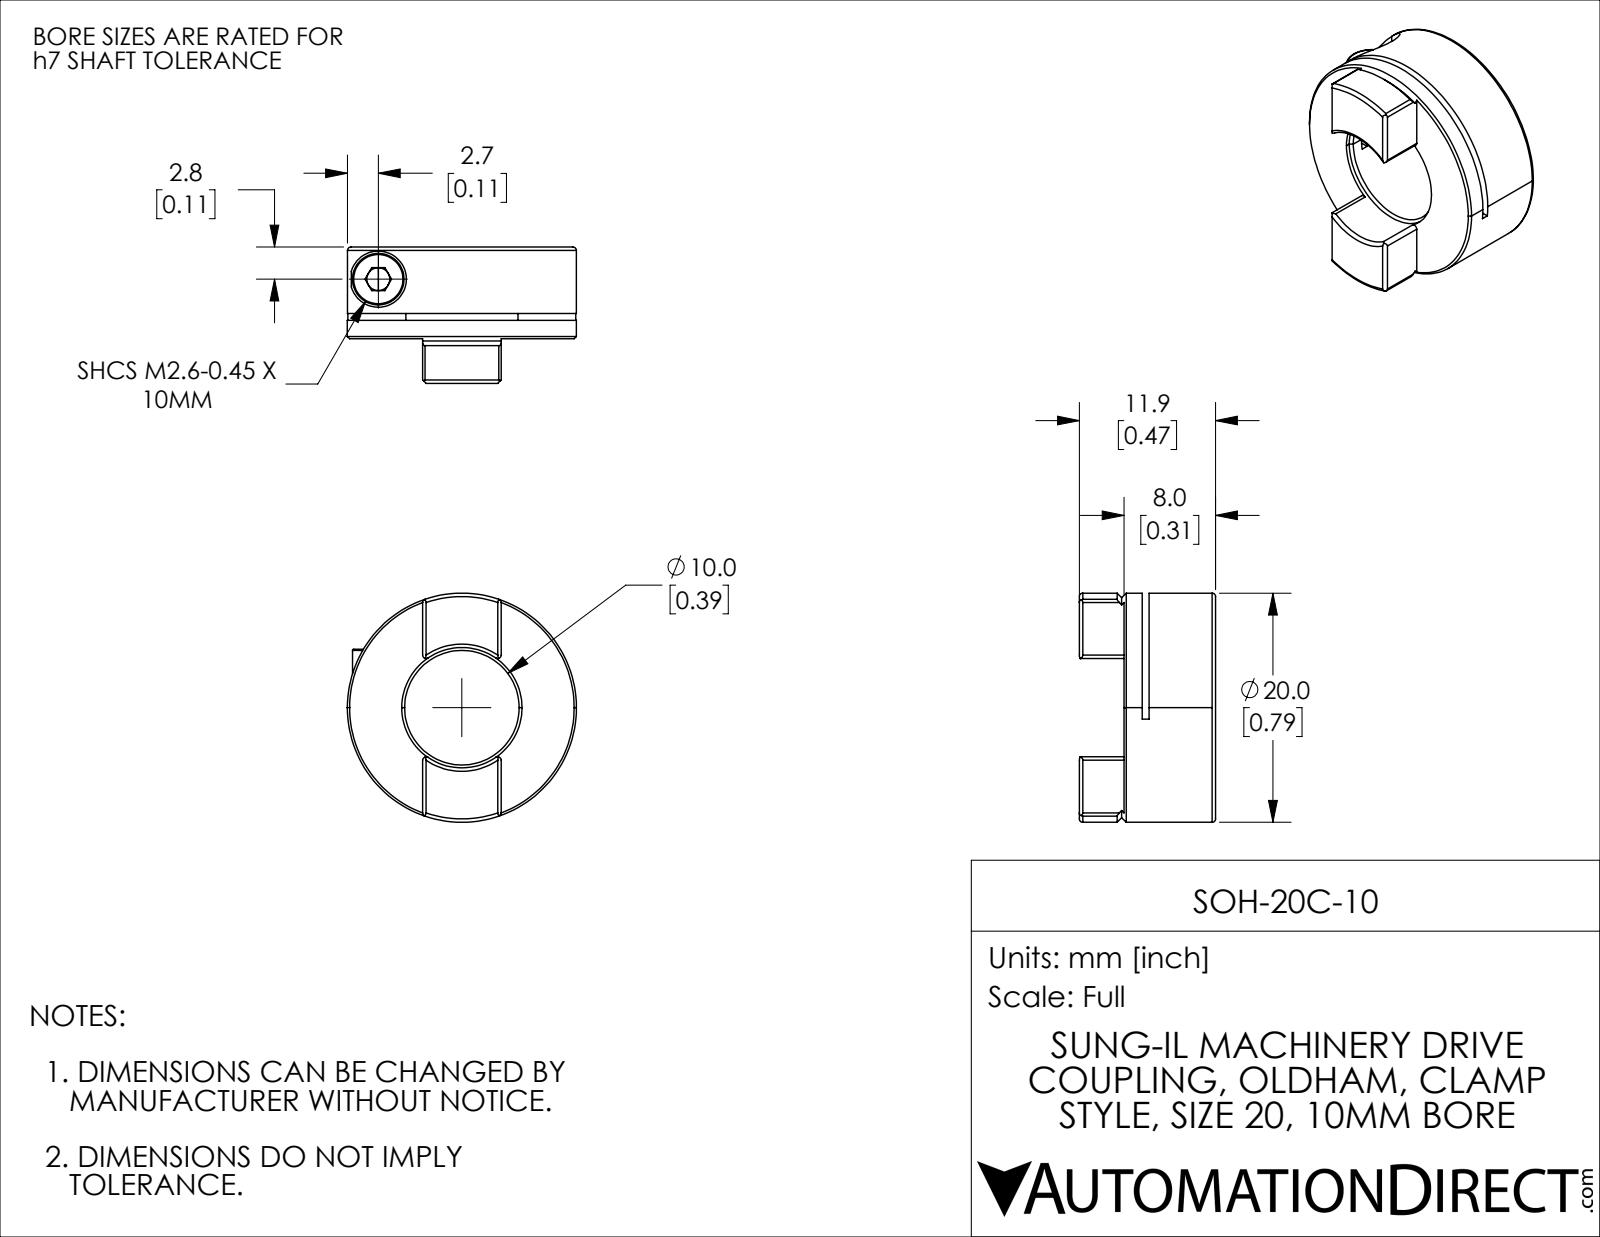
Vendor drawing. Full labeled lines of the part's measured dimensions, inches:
Part name (STEP PRODUCT): SOH-20C-10
STEP written by: SolidWorks 2021 (CONFIG_CONTROL_DESIGN)
Units: inches
Bodies: 2 solids, 97 faces (38 planar, 34 cylindrical, 25 other)
Overall size (bounding box): 0.787 × 0.787 × 0.469
Volume: 0.122 in³ · Surface area: 2.945 in²
Round holes (diameter × count): ⌀0.079 ×1, ⌀0.081 ×1, ⌀0.11 ×1, ⌀0.193 ×1, ⌀0.394 ×1, ⌀0.413 ×1
Round bosses / shafts (diameter × count): ⌀0.787 ×1, ⌀0.177 ×1, ⌀0.102 ×1
Partial cylindrical surfaces — rounded edges, fillets, slot ends (radius × count): R0.012 ×8, R0.886 ×1
Main face-to-face distances: 0.315, 0.252, 0.063, 0.228, 0.024, 0.087, 0.24, 0.469, 0.217, 0.154
